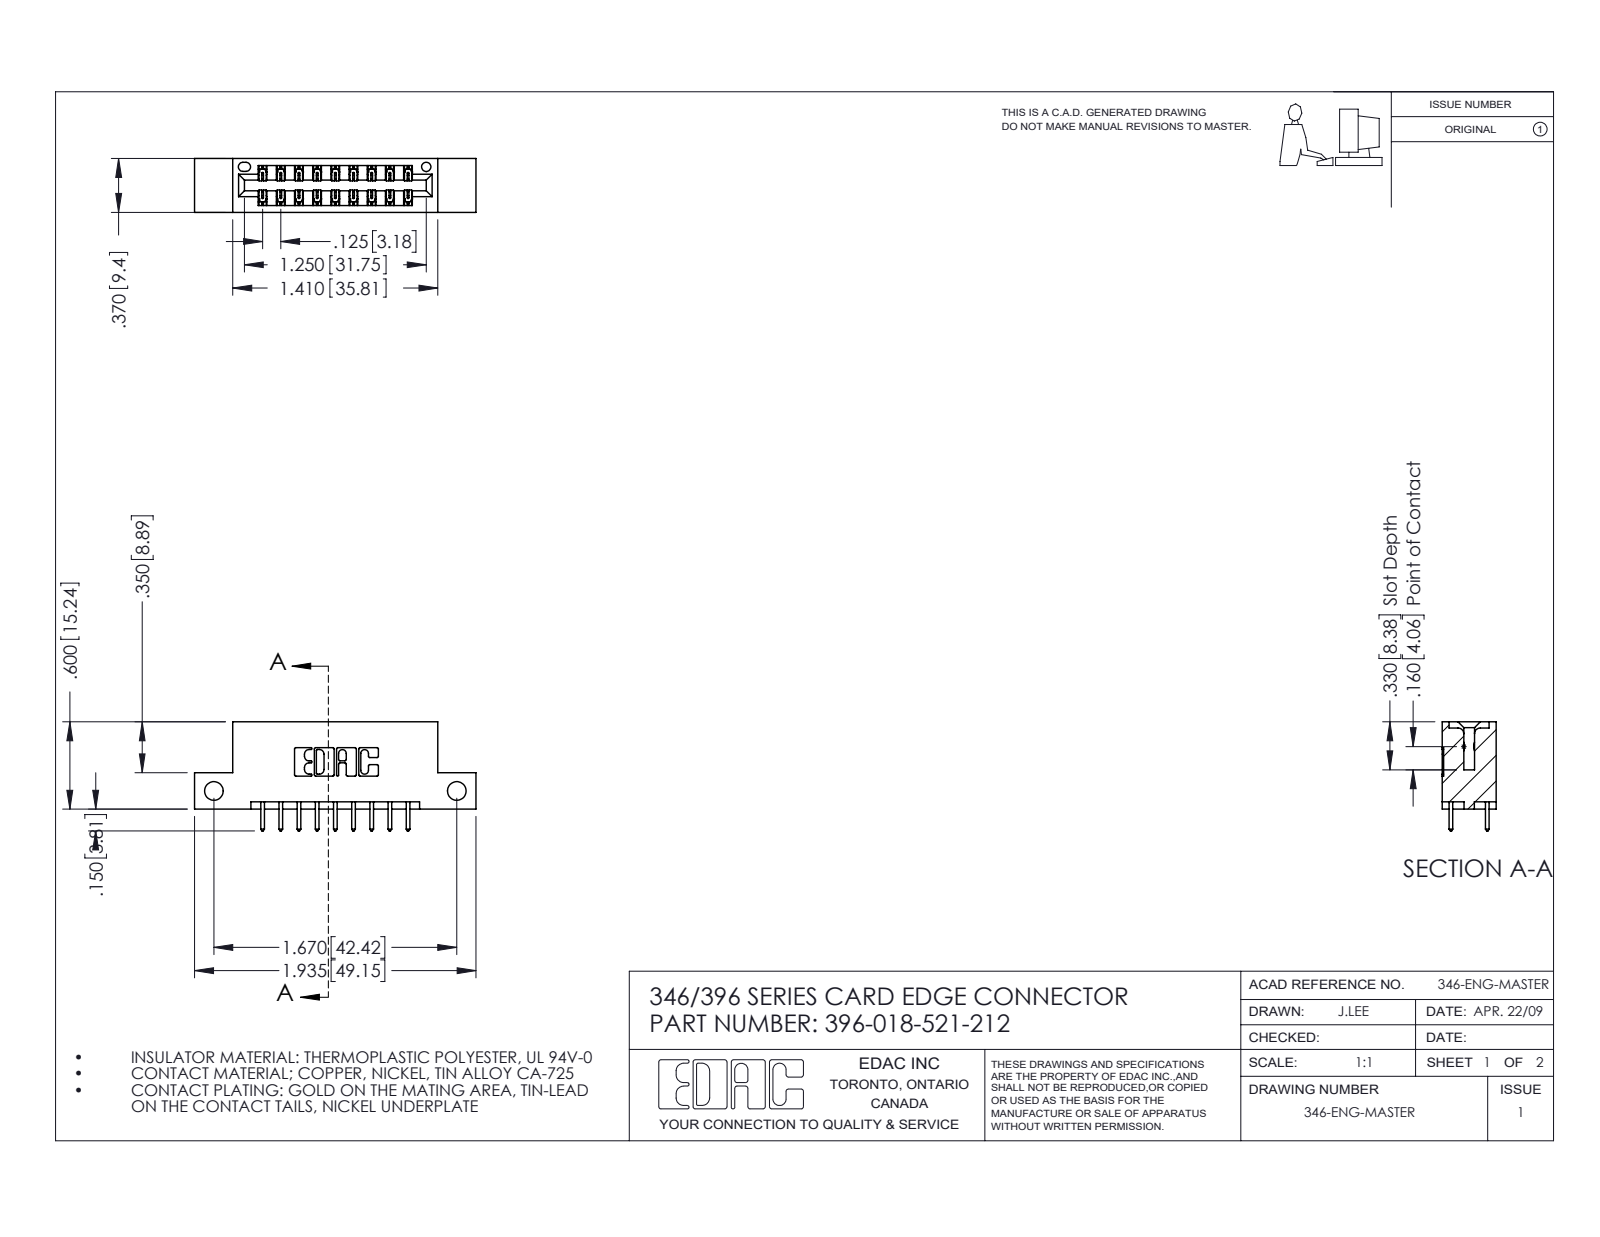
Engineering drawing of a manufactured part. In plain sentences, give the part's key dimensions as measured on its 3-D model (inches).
The part is named "345-292-001_345-293-121; 396-018-521-212; 346 Part_Flush Mounting Lugs - Side Mount". Its 3-D file was written by "SolidWorks 2016 (CONFIG_CONTROL_DESIGN)". It is 19 solids with 1058 faces: 706 planar, 352 cylindrical and 0 other. Overall it measures 1.935 by 0.75 by 0.37 inches. Its volume is 0.271 cubic inches and its surface area 8.37 square inches. Round holes: 2 of diameter 0.128, 1 of diameter 0.064. Partial cylindrical surfaces (rounded edges, fillets, slot ends): 27 of radius 0.006, 22 of radius 0.01, 18 of radius 0.01, 6 of radius 0.007, 6 of radius 0.031, 3 of radius 0.026, 2 of radius 0.014, 2 of radius 0.022. The main face-to-face distances are 0.25, 0.048, 0.322, 0.37, 0.072, 0.298, 0.025, 0.275, 0.148, 0.222. The hole center spacings are 1.67.
